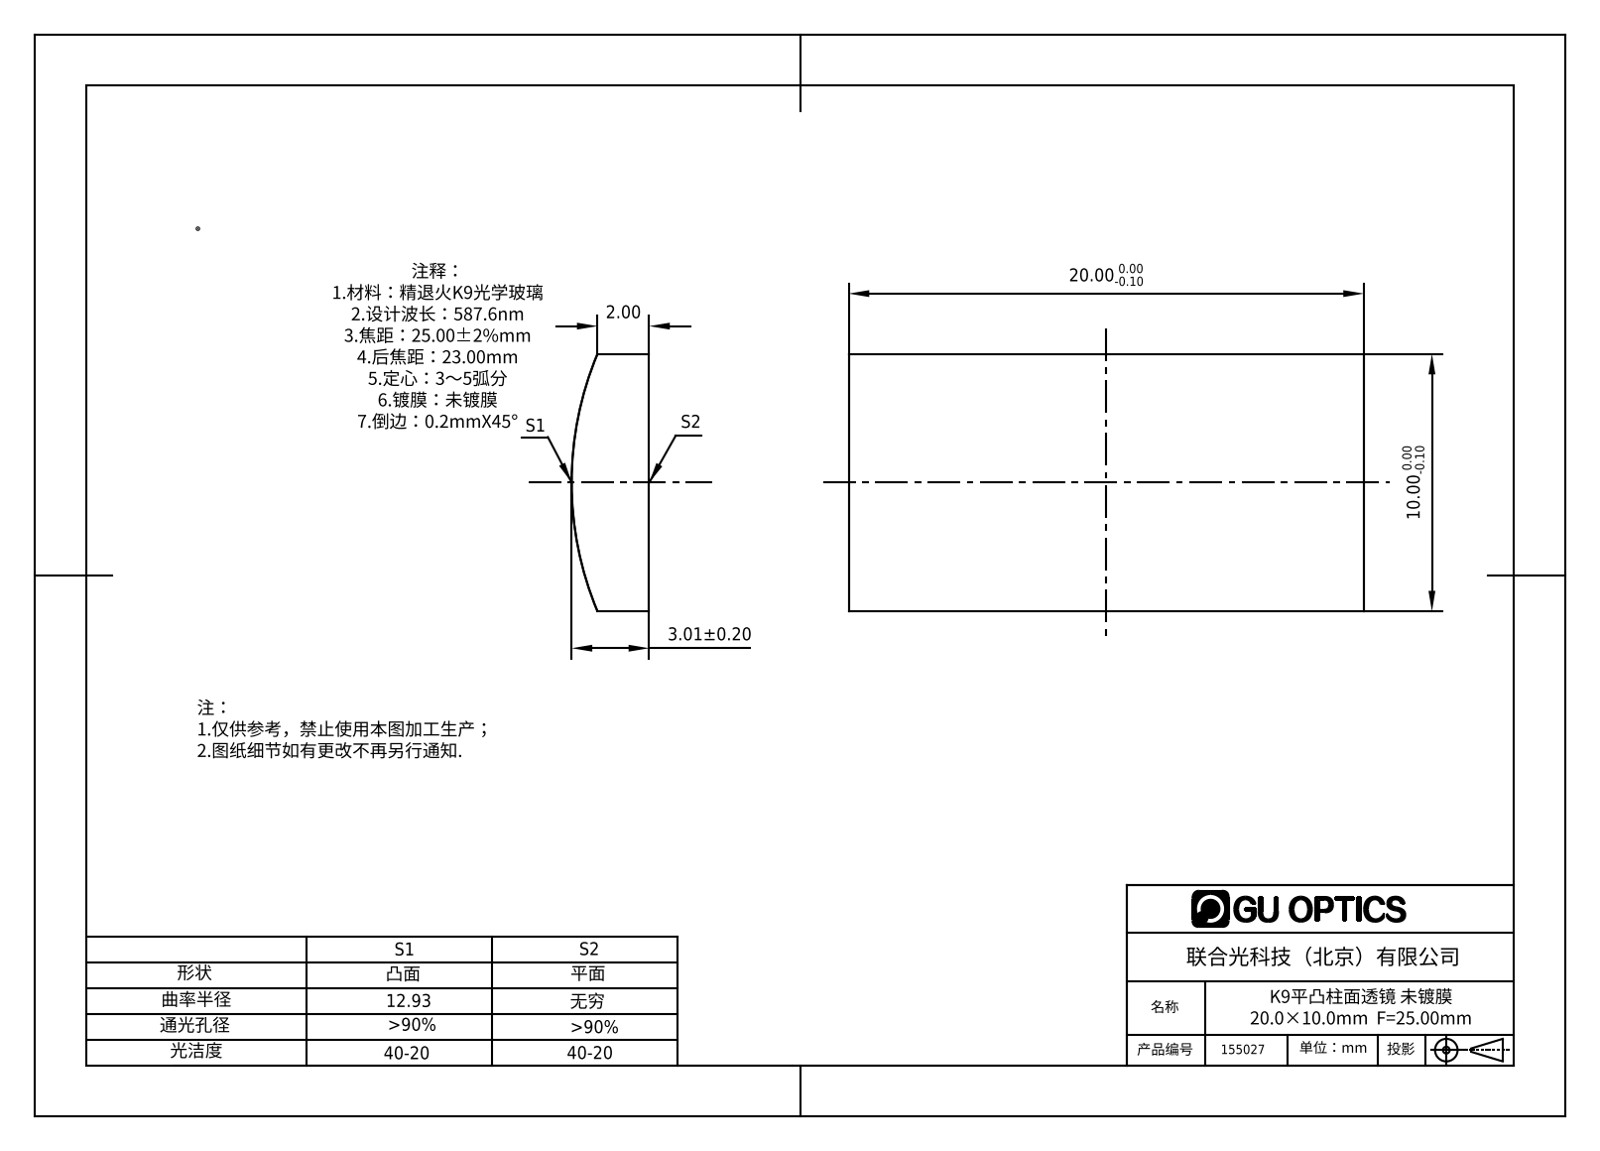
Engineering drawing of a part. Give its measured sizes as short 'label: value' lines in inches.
name: 155027
written by: SolidWorks 2016 (AUTOMOTIVE_DESIGN)
unit: in
bodies: 1 solid, 6 faces (5 planar, 1 cylindrical, 0 other)
size: 0.787 × 0.394 × 0.119
volume: 0.033 in³; area: 0.835 in²
rounds: 1× R0.509
face distances: 0.394, 0.787
